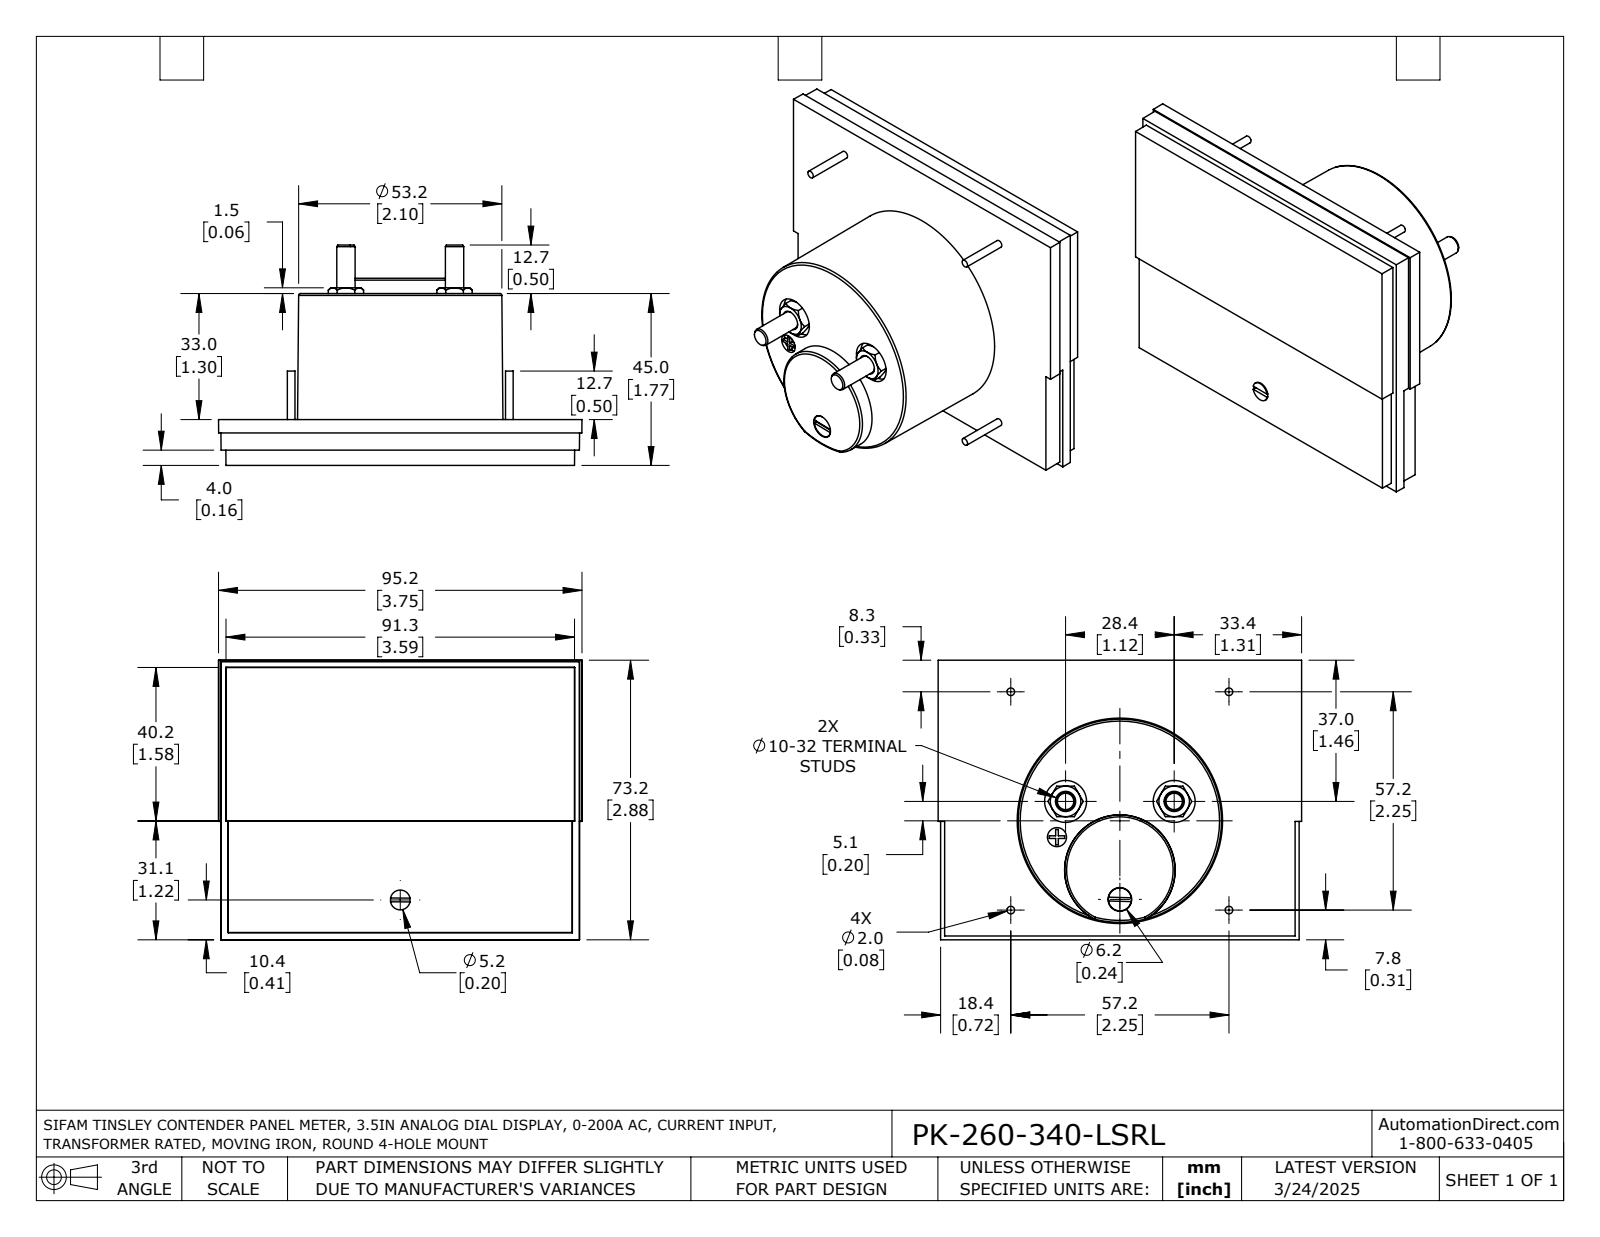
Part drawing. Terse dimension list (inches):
name: PK-260-340-LSRL
written by: SolidWorks 2021 (AUTOMOTIVE_DESIGN)
unit: in
bodies: 1 solid, 163 faces (76 planar, 31 cylindrical, 56 other)
size: 3.748 × 2.882 × 2.272
volume: 9.446 in³; area: 38.39 in²
holes: 2× ⌀0.433, 1× ⌀0.197, 1× ⌀0.244
bosses: 4× ⌀0.079, 2× ⌀0.189, 1× ⌀0.236, 1× ⌀0.205
rounds: 1× R0.1
face distances: 0.472, 0.03, 0.443, 1.772, 1.299, 1.742, 0.157, 0.073, 0.315, 1.457
hole spacings: 1.155, 0.379, 0.912, 1.12, 1.263
